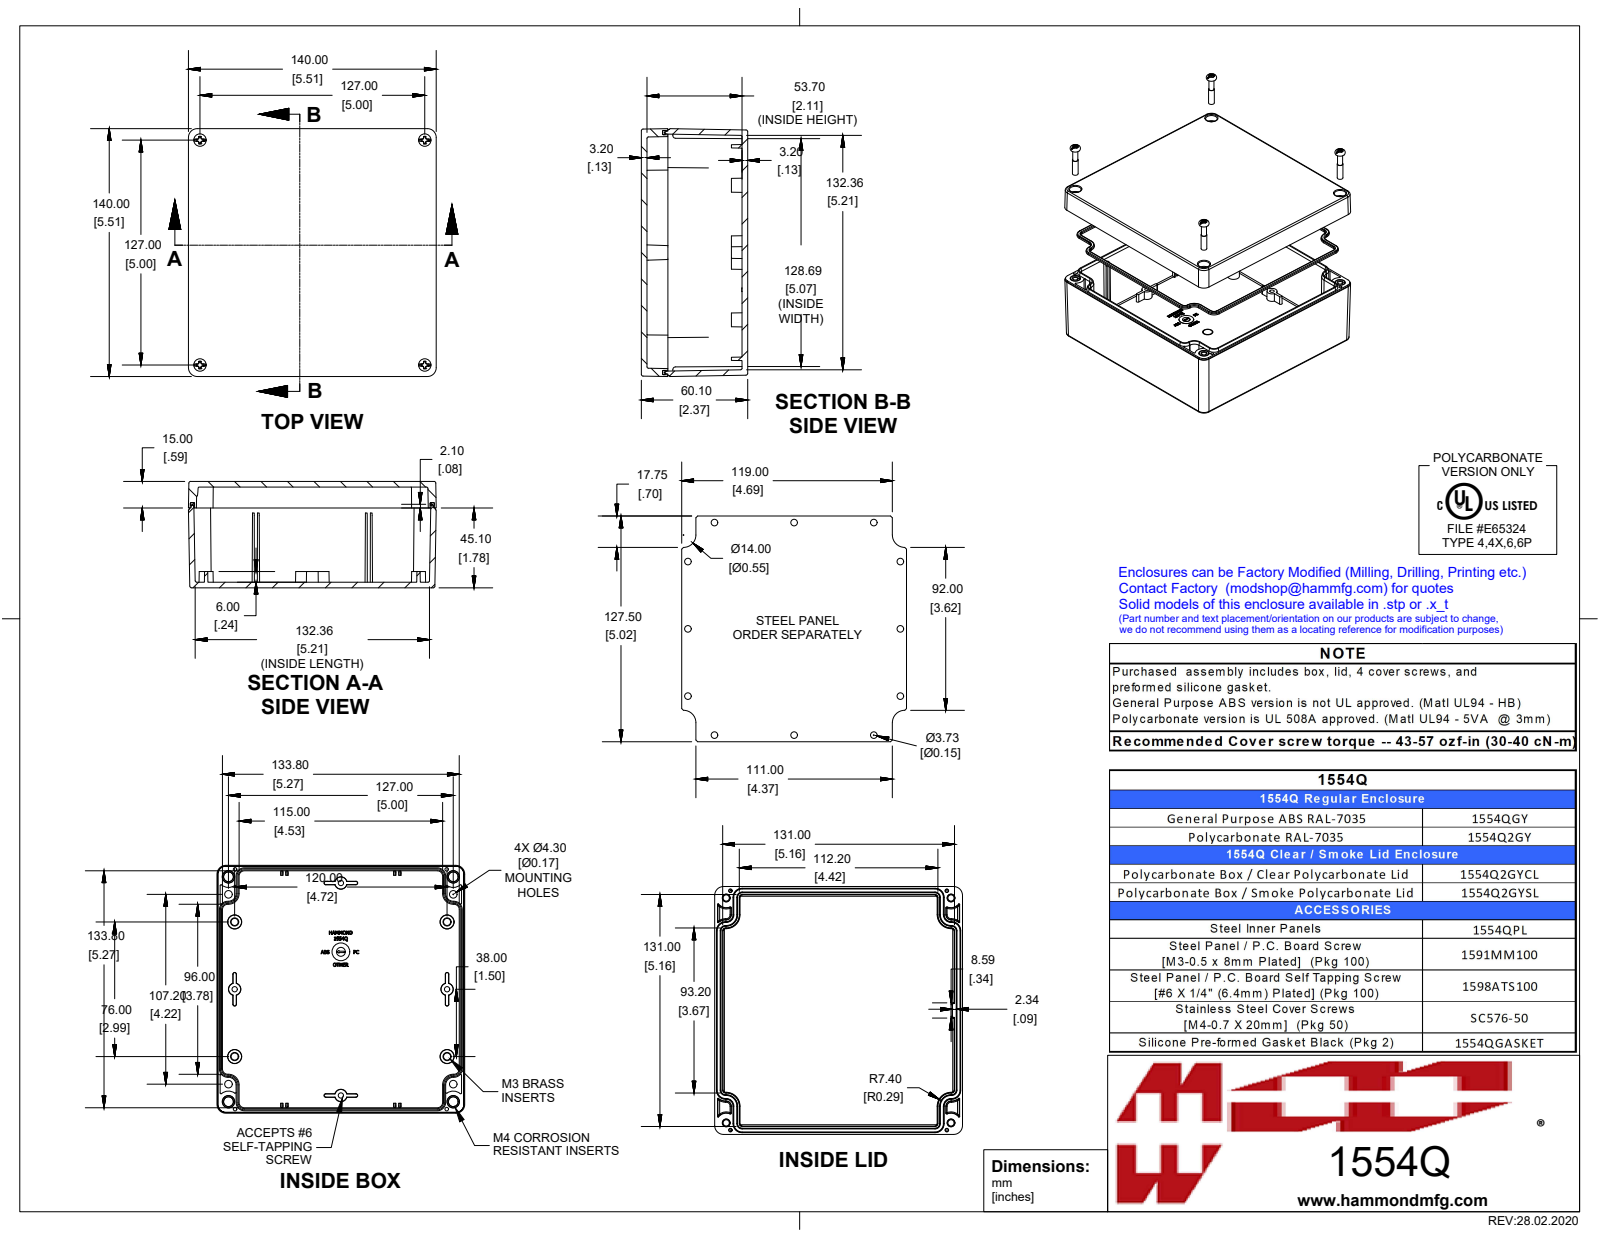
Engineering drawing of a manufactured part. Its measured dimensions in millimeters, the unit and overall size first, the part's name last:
Units: millimetres
Overall size (bounding box): 140 × 140 × 60.1
Round holes (diameter × count): ⌀2.5 ×4, ⌀3.3 ×4, ⌀4.6 ×4
Round bosses / shafts (diameter × count): ⌀6.4 ×4, ⌀5.5 ×4, ⌀5.3 ×4, ⌀4.8 ×4, ⌀3.9 ×4, ⌀3.9 ×4, ⌀3.8 ×4, ⌀3.4 ×4
Partial cylindrical surfaces — rounded edges, fillets, slot ends (radius × count): R0.5 ×26, R0.3 ×20, R1 ×12, R0.8 ×10, R2.6 ×8, R5 ×8, R5.1 ×8, R3 ×4
Main face-to-face distances: 3.2, 56.9, 60.1, 3.1, 53.7, 136.9, 140, 135.5, 4.5, 132.4
Hole centre spacings: 25.7, 101.5, 126.1, 127, 159.9, 76, 120, 142
Volume: 238 800 mm³ · Surface area: 164 000 mm²
Bodies: 15 solids, 1867 faces (610 planar, 374 cylindrical, 883 other)
Part name (STEP PRODUCT): 1554Q2GY
STEP written by: SolidWorks 2019 (AUTOMOTIVE_DESIGN)
